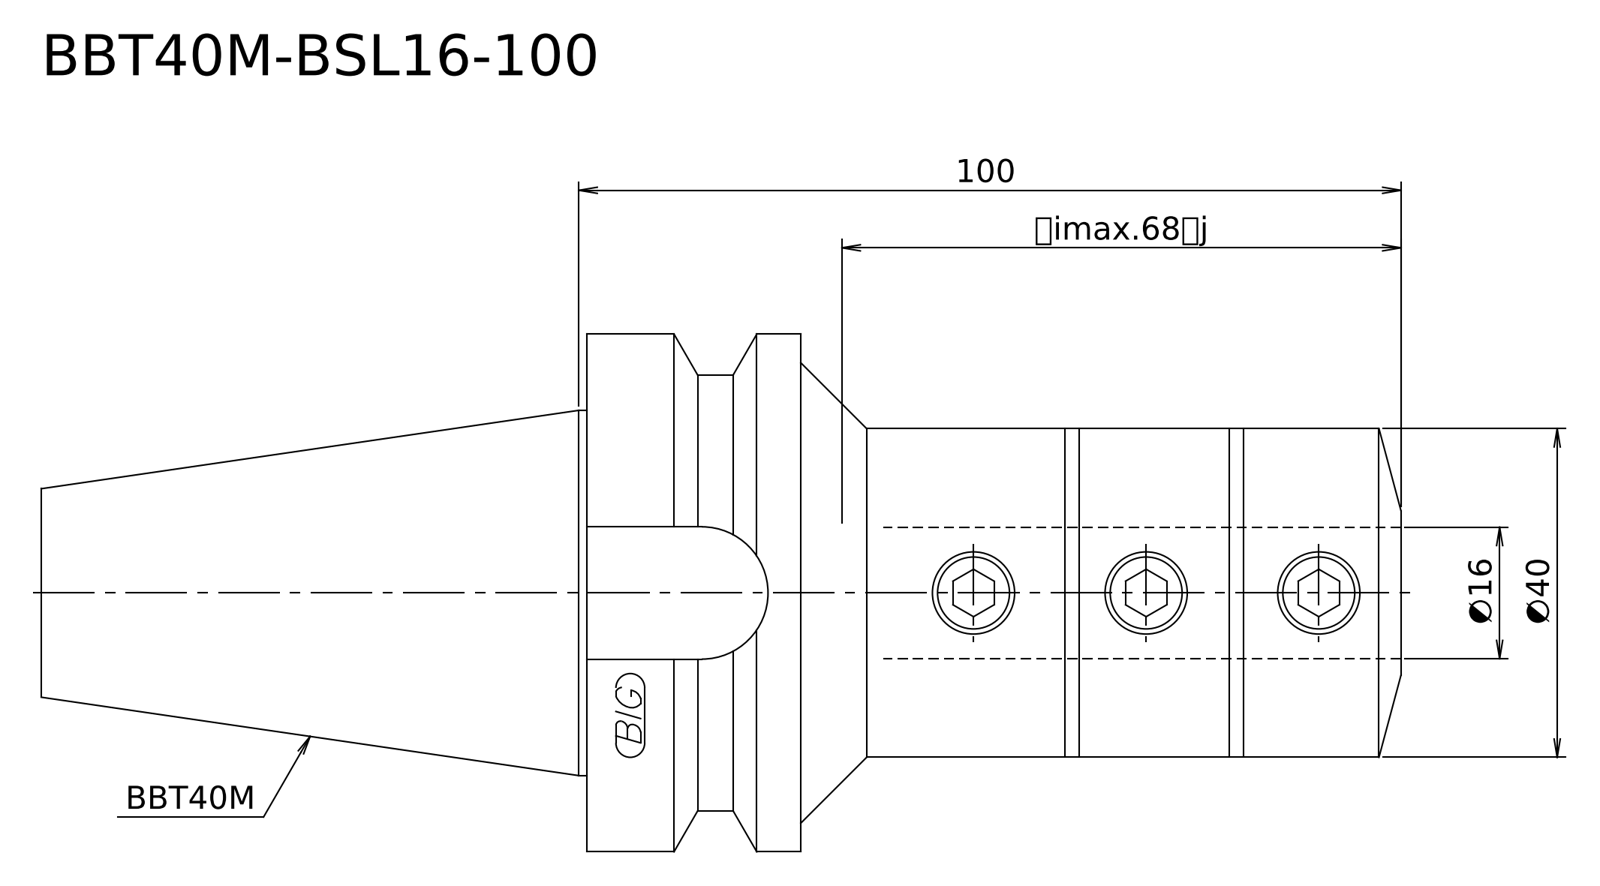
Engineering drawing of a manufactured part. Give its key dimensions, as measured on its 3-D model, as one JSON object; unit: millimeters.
{"step_written_by": "Kubotek KeyCreator 2011 V10.0.2 (22737) (automotive_design)", "units": "millimeters", "bodies": {"solids": 1, "faces": 14, "planar": 4, "cylindrical": 5, "other": 5}, "overall_size": [165.4, 63, 63], "volume_mm3": 235035, "surface_area_mm2": 26914, "round_bosses_or_shafts": [[63, 1], [53, 1], [44.45, 1], [40, 1]], "face_to_face_distances": [26, 92.4, 66.4, 73, 99, 165.4]}
